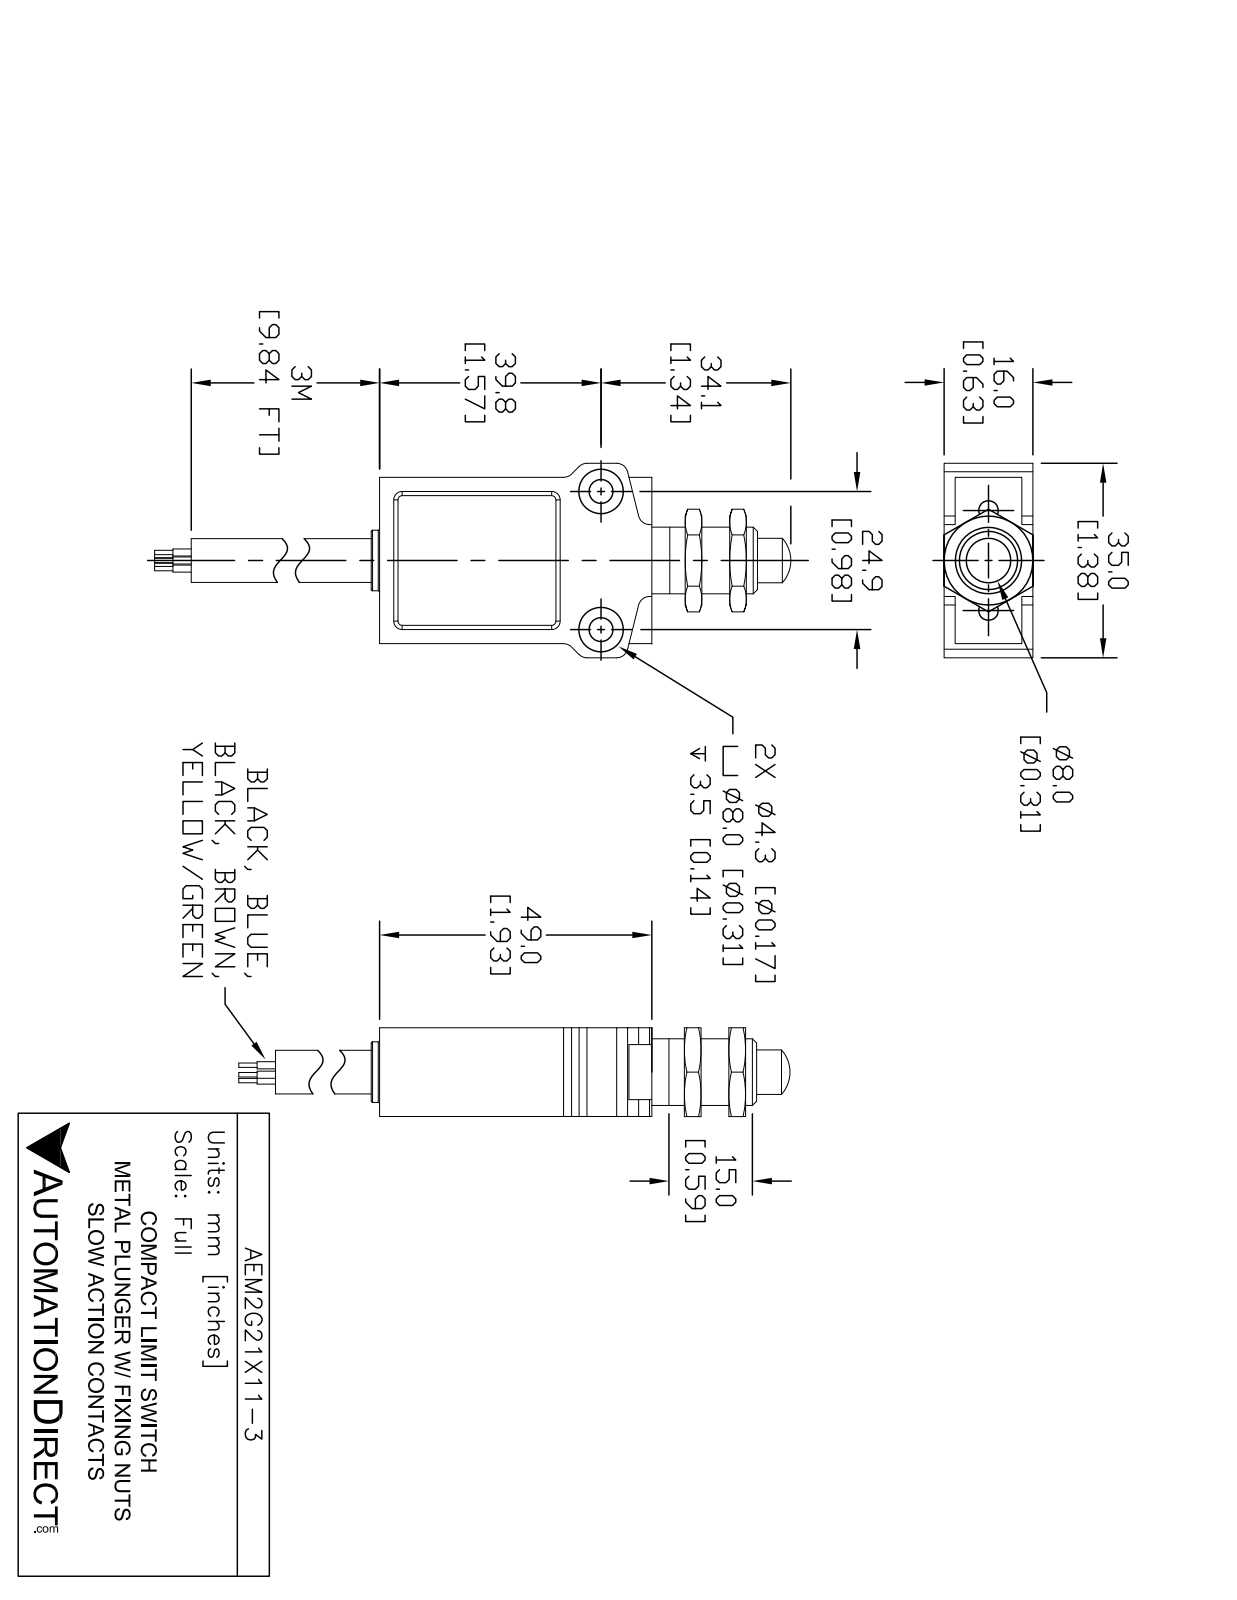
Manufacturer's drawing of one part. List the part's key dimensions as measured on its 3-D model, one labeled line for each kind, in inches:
Part name (STEP PRODUCT): AEM2G21X11-3_Default
STEP written by: SolidWorks 2021 (CONFIG_CONTROL_DESIGN)
Units: inches
Bodies: 1 solid, 168 faces (84 planar, 43 cylindrical, 41 other)
Overall size (bounding box): 3.53 × 1.38 × 0.63
Volume: 1.525 in³ · Surface area: 13.02 in²
Round holes (diameter × count): ⌀0.177 ×2, ⌀0.344 ×2
Round bosses / shafts (diameter × count): ⌀0.05 ×5, ⌀0.031 ×5, ⌀0.47 ×1, ⌀0.43 ×1, ⌀0.31 ×1
Partial cylindrical surfaces — rounded edges, fillets, slot ends (radius × count): R0.03 ×8, R0.08 ×8
Main face-to-face distances: 0.03, 0.6, 0.57, 0.63, 1.18, 0.12, 0.3, 1.93, 0.187, 0.443
Hole centre spacings: 0.98
